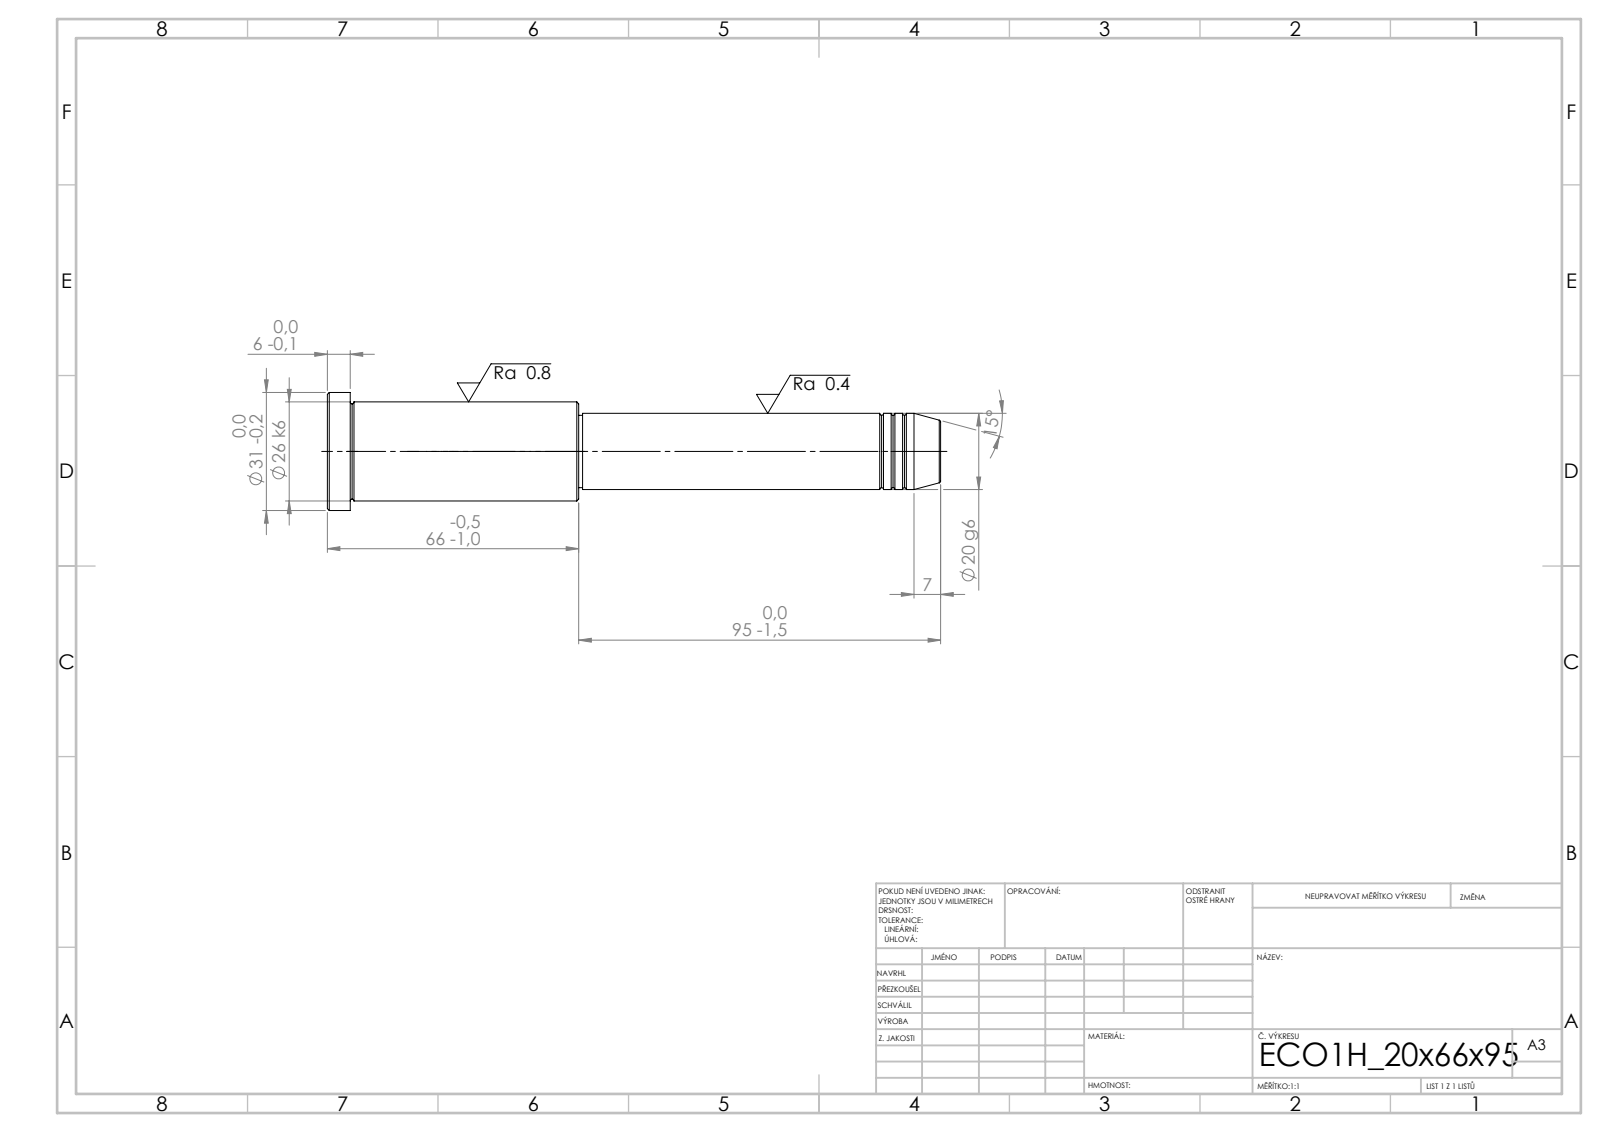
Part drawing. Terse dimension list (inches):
written by: SolidWorks 2019 (CONFIG_CONTROL_DESIGN)
unit: in
bodies: 1 solid, 43 faces (5 planar, 14 cylindrical, 24 other)
size: 6.339 × 1.22 × 1.22
volume: 4.008 in³; area: 20.11 in²
bosses: 1× ⌀1.22, 1× ⌀1.024, 1× ⌀0.787, 1× ⌀0.748
face distances: 0.236, 2.362, 2.598, 3.74, 6.102, 6.339, 3.701, 0.039, 2.402, 2.638
